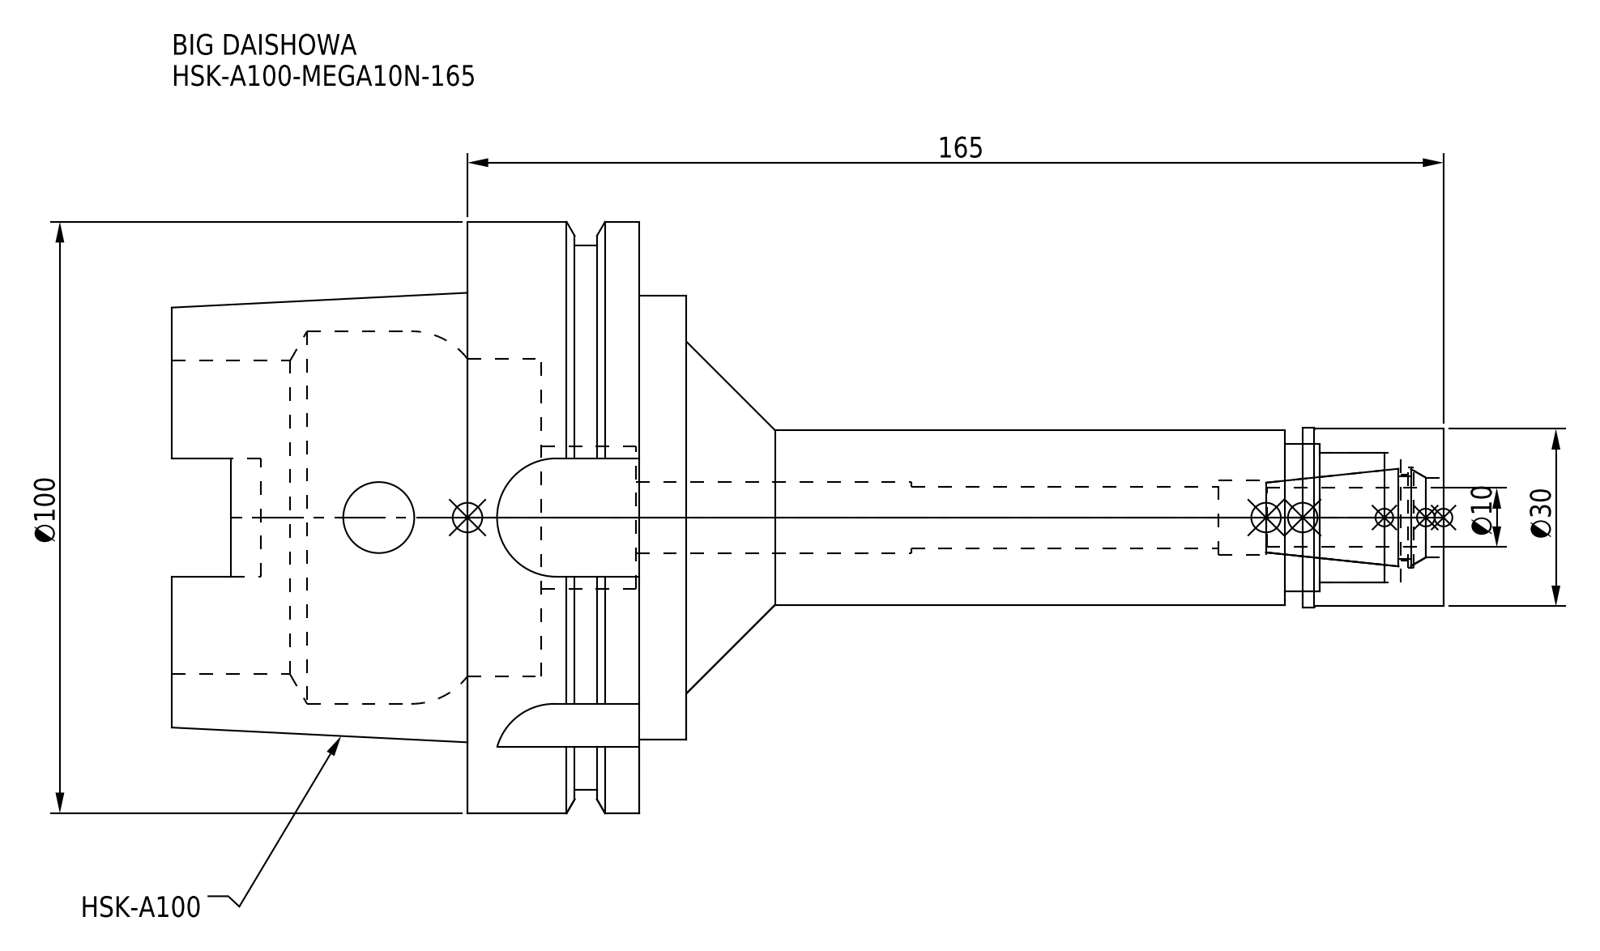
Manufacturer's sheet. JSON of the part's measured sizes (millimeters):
{"part_name": "HA100MN10165-100_ASM.stp; HSK-A100-MEGA10N-165-100.stp; HSK-A100-MEGA10N-165-100-FreeParts; HSK-A100-MEGA10N-165_1.stp (+3 more)", "step_written_by": "SolidWorks 2019 (CONFIG_CONTROL_DESIGN)", "units": "millimeters", "bodies": {"solids": 2, "faces": 124, "planar": 44, "cylindrical": 58, "other": 22}, "overall_size": [215, 100, 100], "volume_mm3": 374458, "surface_area_mm2": 71346, "round_holes": [[12, 2], [10.4, 1], [12.5, 1], [13.5, 1], [14.5, 1], [17, 1], [22, 1], [24, 1], [25, 1], [53, 1], [53.8, 1], [63, 1]], "round_bosses_or_shafts": [[100, 1], [92, 1], [75, 1], [30.3, 1], [30, 1], [29.5, 1]], "partial_cylinders_radius": [[4.88, 4], [10, 4]], "face_to_face_distances": [29, 16.55, 12.45, 8, 24.55, 37, 87, 79, 62.45, 50]}
